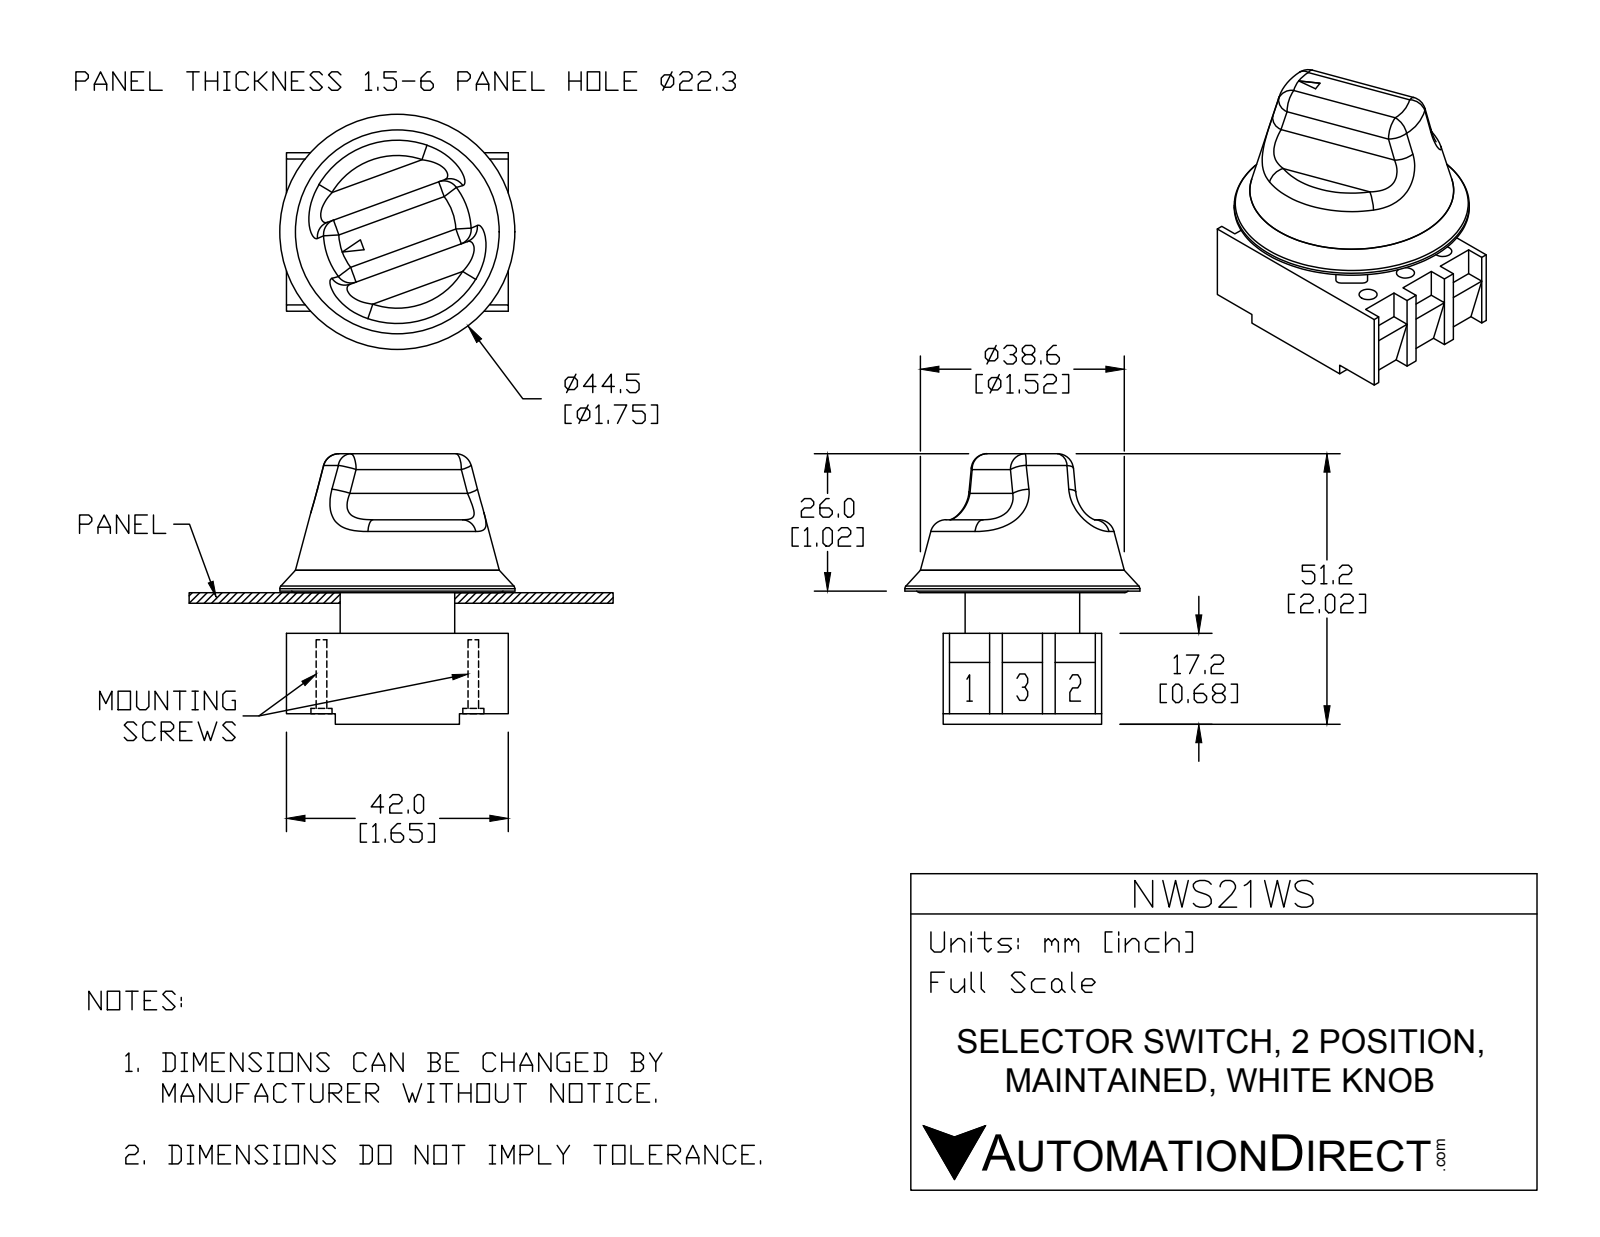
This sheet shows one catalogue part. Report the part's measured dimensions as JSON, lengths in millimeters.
{"part_name": "NWS21WS", "step_written_by": "SolidWorks 2015 (AUTOMOTIVE_DESIGN)", "units": "millimeters", "bodies": {"solids": 7, "faces": 236, "planar": 134, "cylindrical": 67, "other": 35}, "overall_size": [51.2, 44.5, 44.5], "volume_mm3": 35027, "surface_area_mm2": 19099, "round_holes": [[3.4, 6], [5, 6], [12.5, 1]], "round_bosses_or_shafts": [[4.6, 2], [4, 2], [44.5, 1], [21.7, 1]], "partial_cylinders_radius": [[1, 8], [8.7, 5], [3, 2], [5, 2], [11, 1]], "face_to_face_distances": [3.95, 30, 8, 11.95, 7.7, 4.25, 10, 15.2, 22.9, 23.2], "hole_center_spacings": [10, 17.52, 30.45, 28.76, 14.38, 20, 35.03]}
